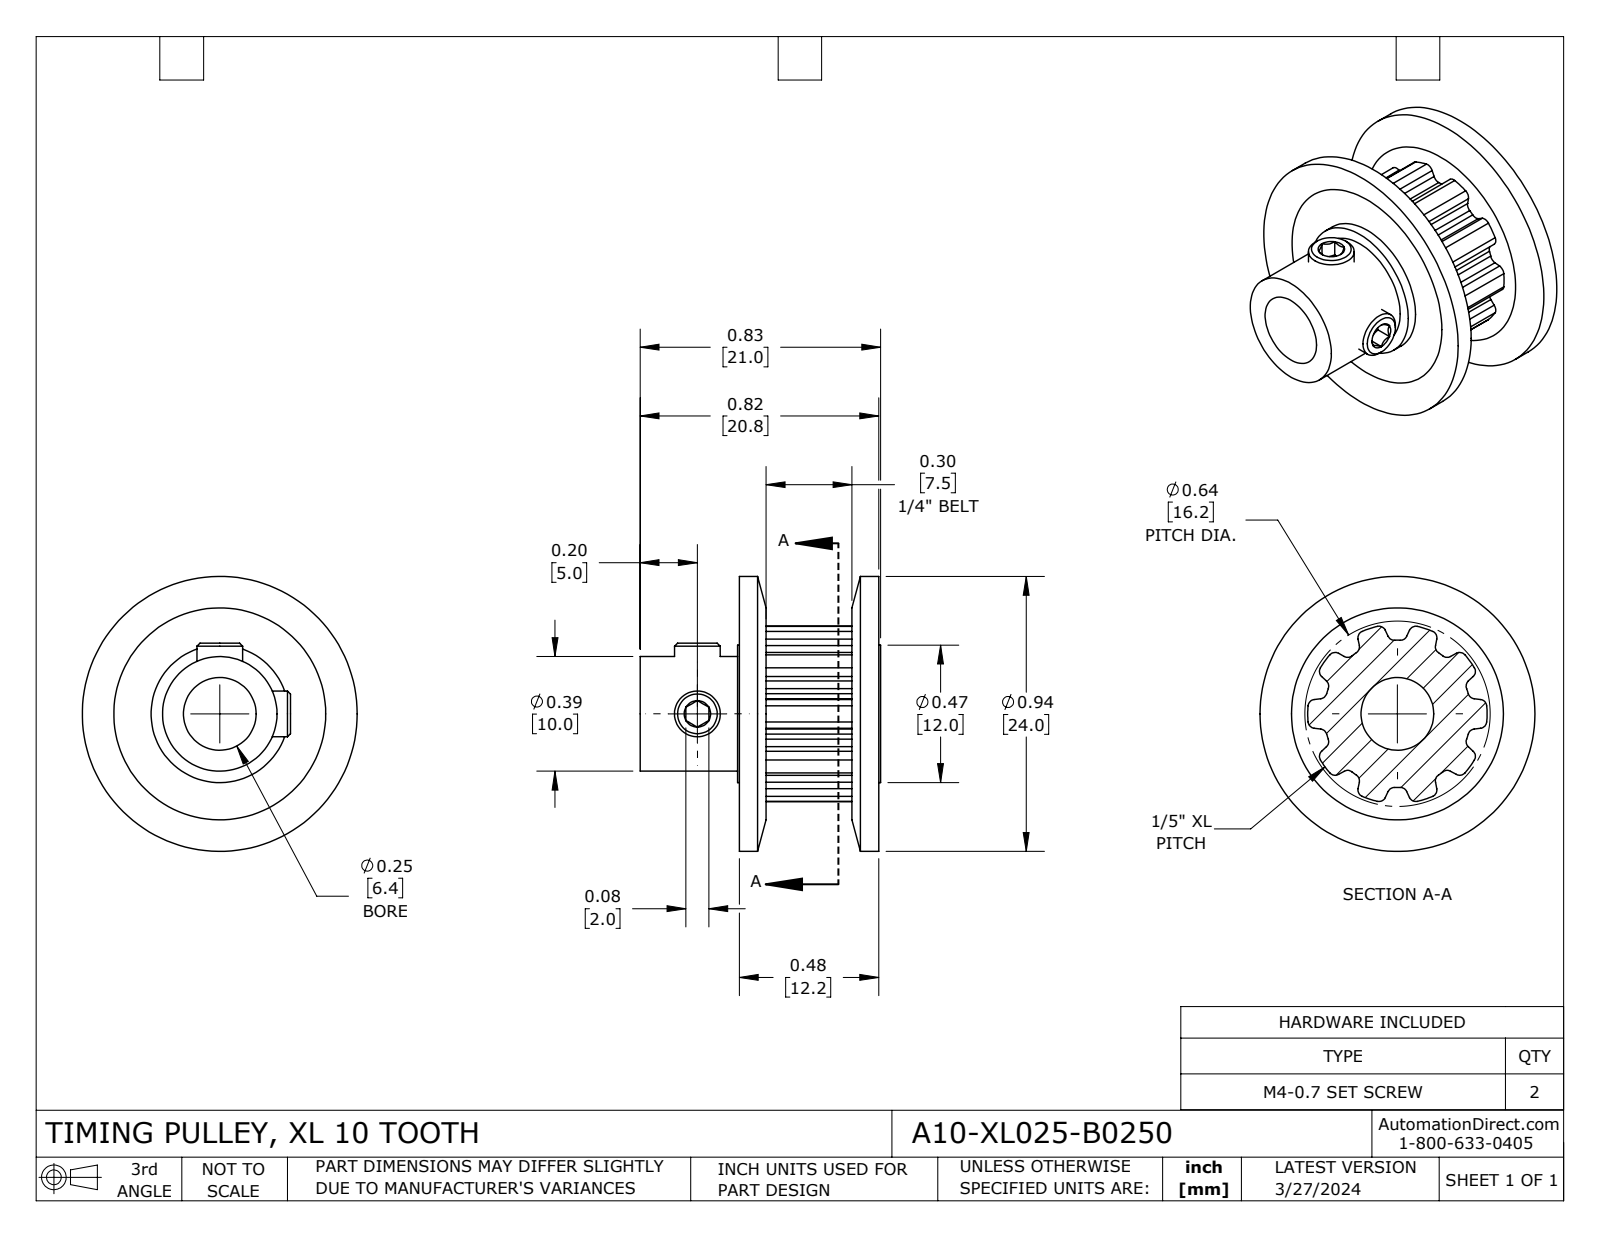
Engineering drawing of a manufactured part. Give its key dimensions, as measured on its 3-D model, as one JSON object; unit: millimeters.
{"part_name": "A10-XL025-B0250", "step_written_by": "SolidWorks 2021 (CONFIG_CONTROL_DESIGN)", "units": "millimeters", "bodies": {"solids": 5, "faces": 172, "planar": 45, "cylindrical": 93, "other": 34}, "overall_size": [24, 24, 21], "volume_mm3": 2922, "surface_area_mm2": 3480, "round_holes": [[3.3, 2], [6.35, 1], [12, 1]], "round_bosses_or_shafts": [[4, 2], [24, 1], [10, 1]], "partial_cylinders_radius": [[0.61, 40], [6.43, 1], [7.83, 1]], "face_to_face_distances": [1.6, 9.1, 7.5, 10.7, 2.5, 0.9, 10, 11.6, 21, 20.1]}
